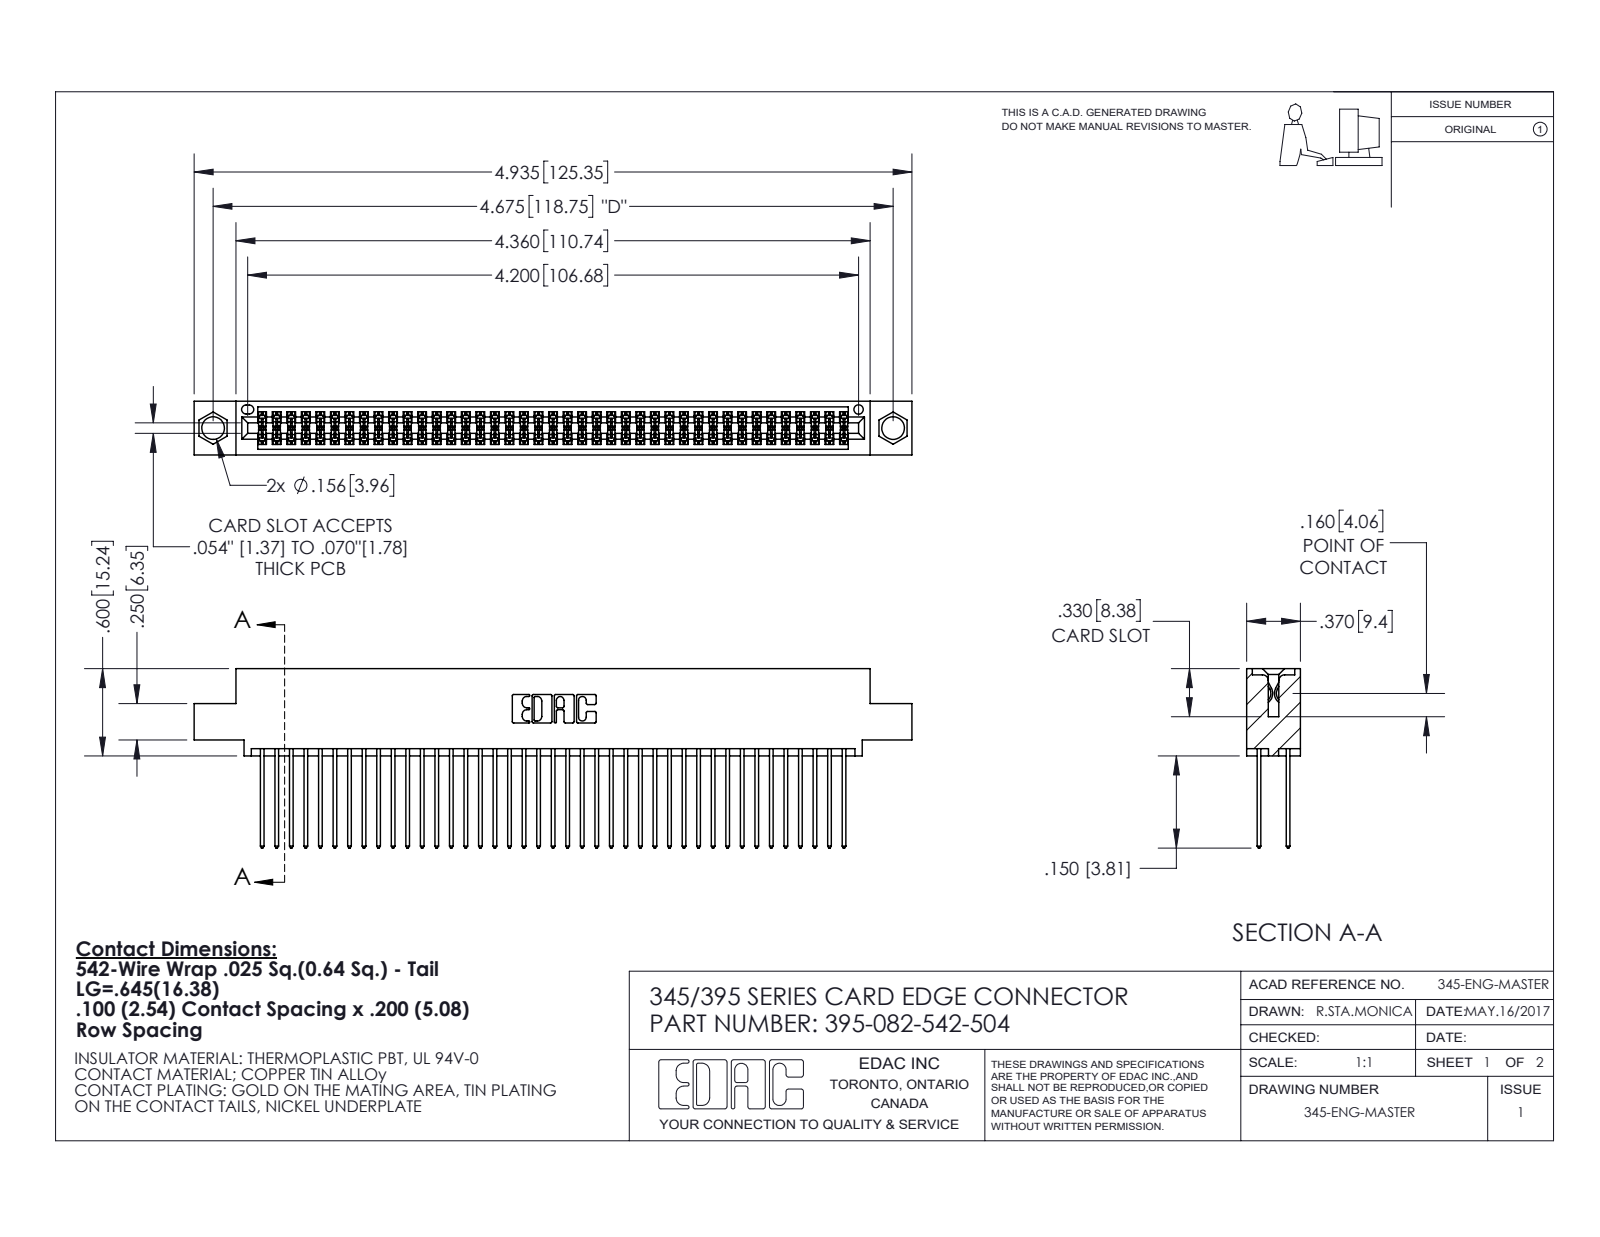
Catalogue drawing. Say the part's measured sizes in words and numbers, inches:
The part is named "345-292-001_345-293-142; 395-082-542-504; 345 Part_0.110 Offset - 0.156 Dia-TI". Its 3-D file was written by "SolidWorks 2020 (CONFIG_CONTROL_DESIGN)". It is 83 solids with 4244 faces: 2804 planar, 1440 cylindrical and 0 other. Overall it measures 4.935 by 1.232 by 0.37 inches. Its volume is 0.755 cubic inches and its surface area 30.99 square inches. Round holes: 2 of diameter 0.156, 1 of diameter 0.064. Partial cylindrical surfaces (rounded edges, fillets, slot ends): 123 of radius 0.006, 82 of radius 0.01, 22 of radius 0.01, 6 of radius 0.007, 6 of radius 0.031, 3 of radius 0.026, 2 of radius 0.014, 2 of radius 0.019. The main face-to-face distances are 0.298, 0.072, 0.2, 0.098, 0.272, 0.025, 0.225, 0.37, 0.175, 0.149. The hole center spacings are 0.27, 4.439, 4.675.
